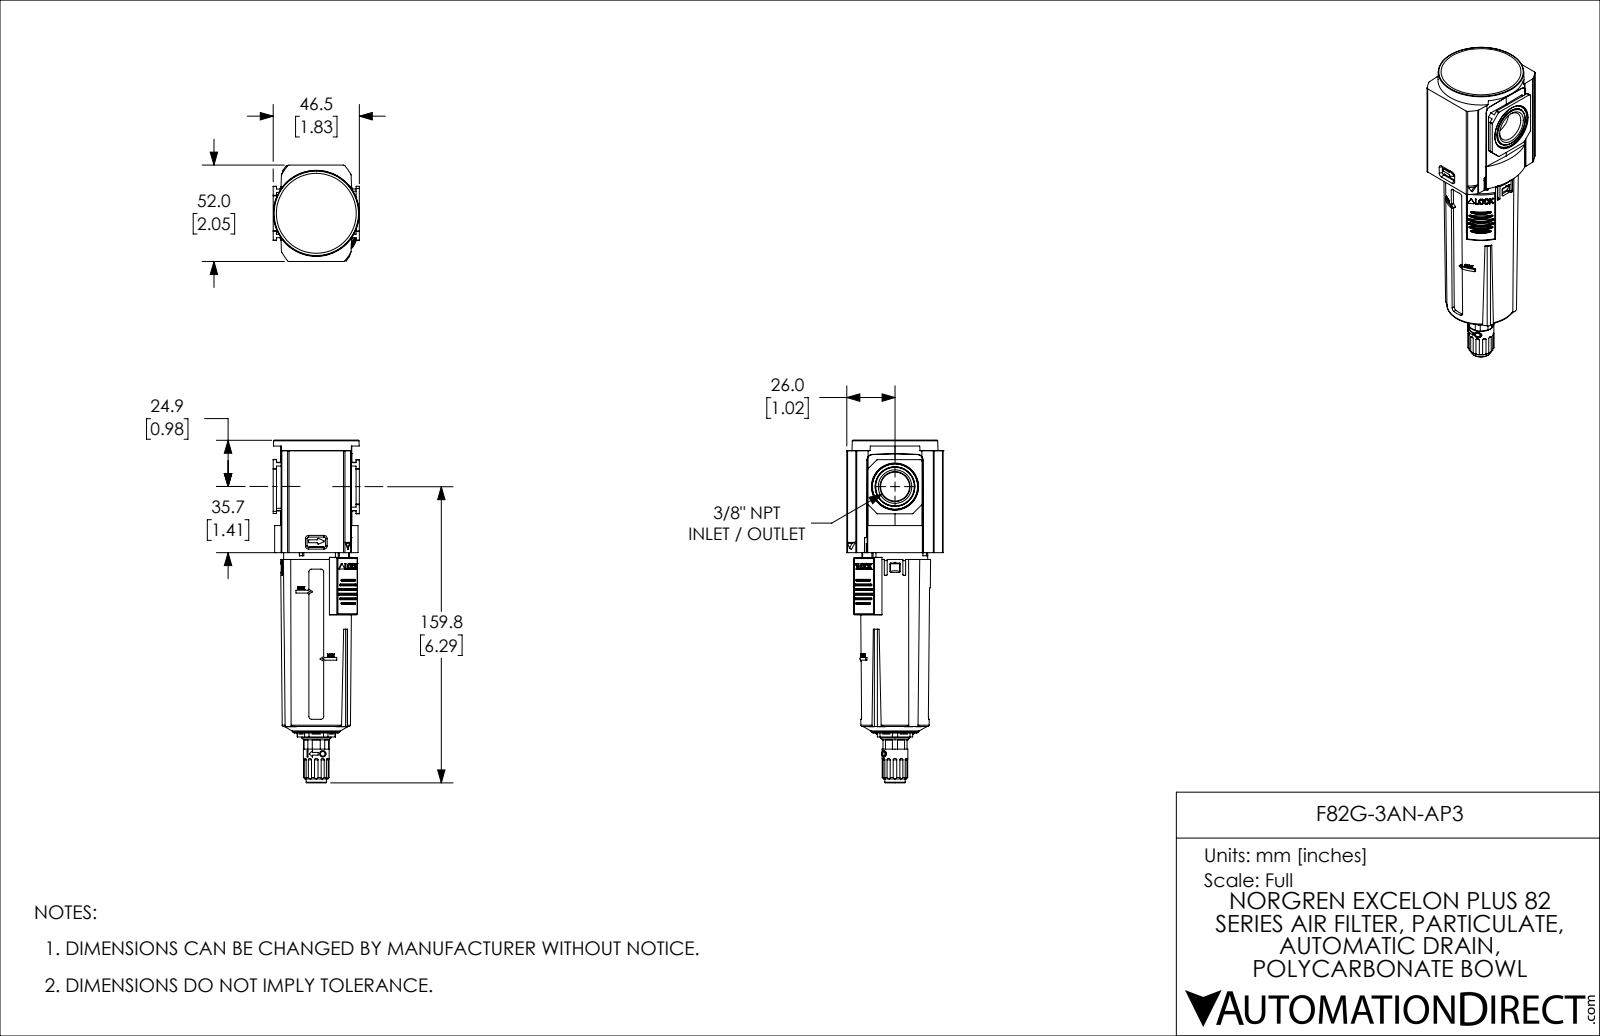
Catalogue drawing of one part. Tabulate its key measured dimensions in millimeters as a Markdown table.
| quantity | value |
| --- | --- |
| part name | F82G-3AN-AP3 |
| STEP written by | SolidWorks 2021 (CONFIG_CONTROL_DESIGN) |
| units | millimeters |
| bodies | 5 solids, 1179 faces (508 planar, 428 cylindrical, 243 other) |
| overall size | 184.8 × 52 × 46.5 |
| volume | 215 800 mm³ |
| surface area | 57 310 mm² |
| round holes (diameter × count) | 3.3 × 2, 2.5 × 1, 6.6 × 1, 16 × 1 |
| round bosses / shafts (diameter × count) | 35.3 × 1, 34.4 × 1, 32.8 × 1, 31.9 × 1, 15.7 × 1, 13.9 × 1, 13.7 × 1, 11 × 1 |
| partial cylindrical surfaces (radius × count) | 0.5 × 59, 1 × 49, 0.3 × 11, 0.2 × 10, 0.3 × 10, 0.8 × 8, 0.9 × 8, 1.2 × 8 |
| main face-to-face distances | 1.5, 50.5, 37.3, 52, 49, 1.5, 53.2, 54.6, 4.6, 37.5 |
| hole center spacings | 15.1, 30.2 |
